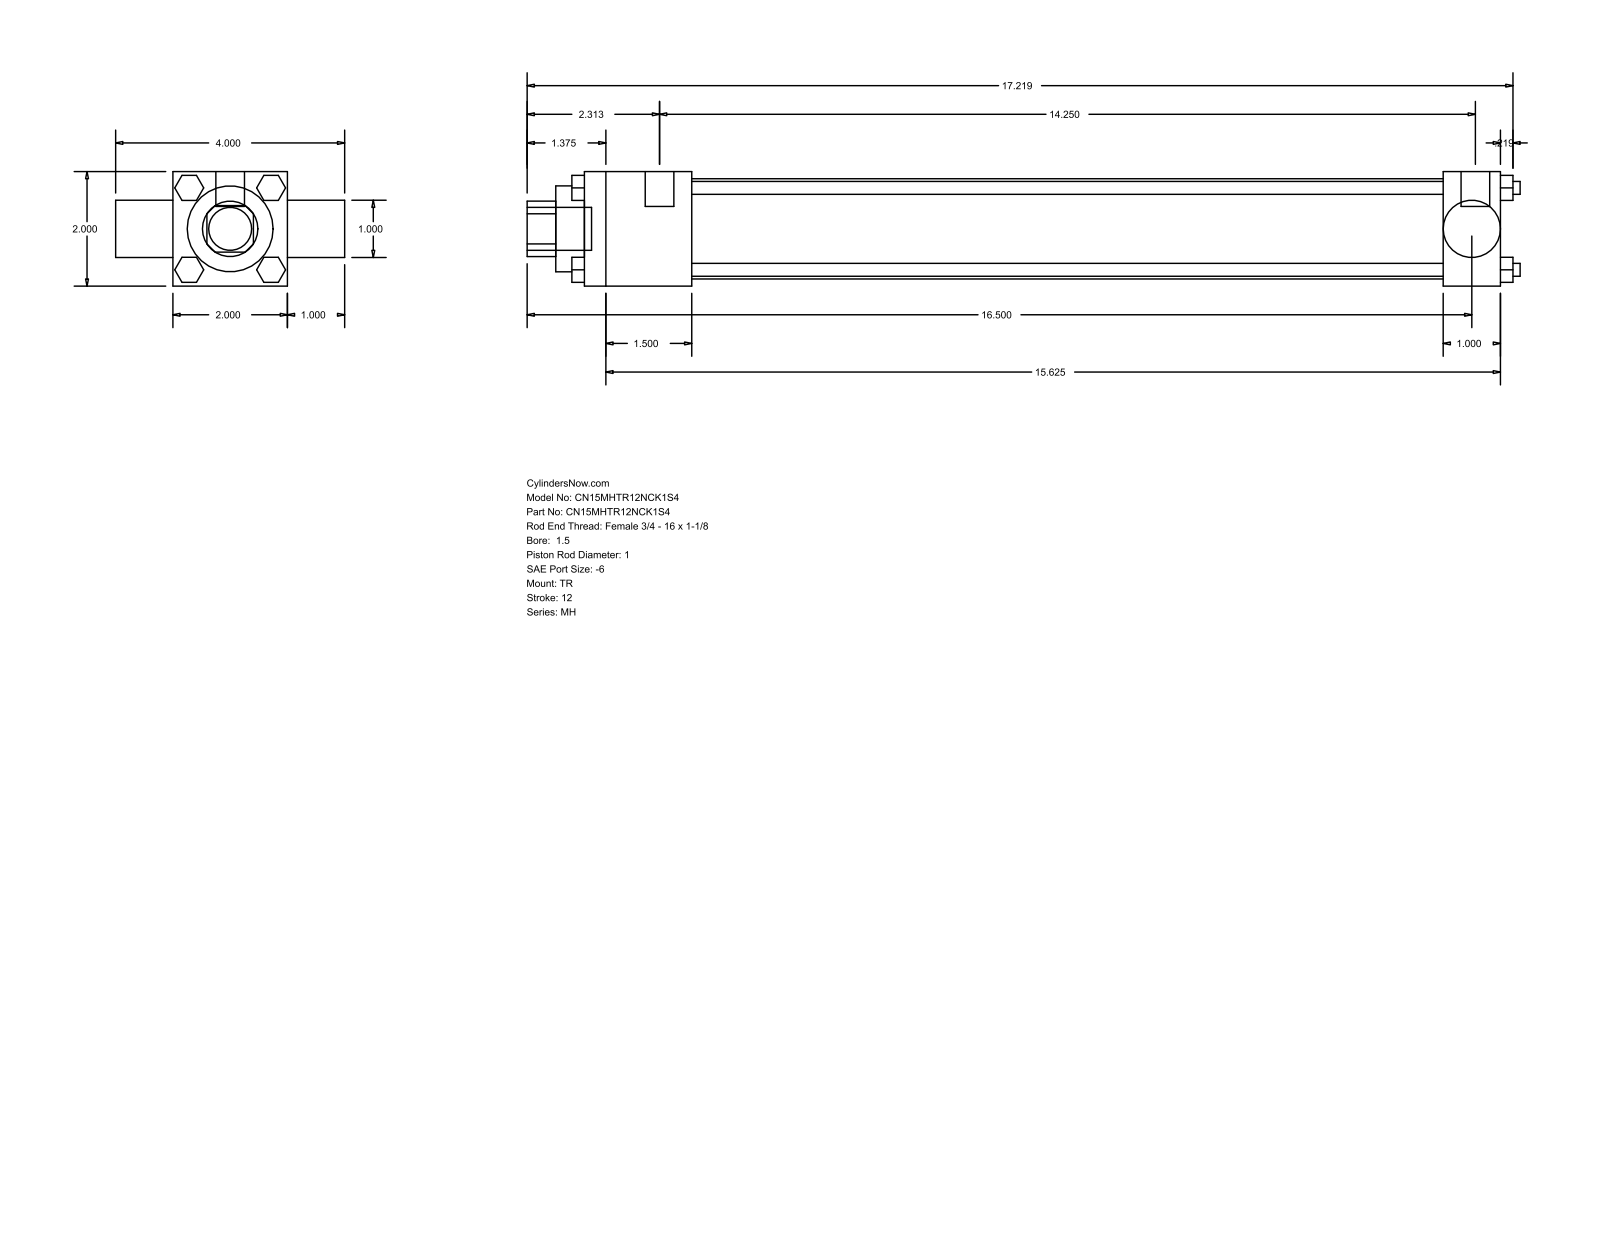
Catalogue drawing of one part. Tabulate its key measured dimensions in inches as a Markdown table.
| quantity | value |
| --- | --- |
| part name | MH_TR__0150_1 |
| STEP written by | GSSL Pune (CONFIG_CONTROL_DESIGN) |
| units | inches |
| bodies | 0 solids, 120 faces (92 planar, 28 cylindrical, 0 other) |
| overall size | 17.344 × 4 × 2 |
| round holes (diameter × count) | 0.998 × 1, 1 × 1, 1.5 × 1, 1.75 × 1 |
| round bosses / shafts (diameter × count) | 0.225 × 4, 0.219 × 3, 0.5 × 2, 0.75 × 1 |
| partial cylindrical surfaces (radius × count) | 0.484 × 1 |
| main face-to-face distances | 2, 1, 16, 3, 1.875, 14.125, 15, 13.125, 16.219, 0.5 |
